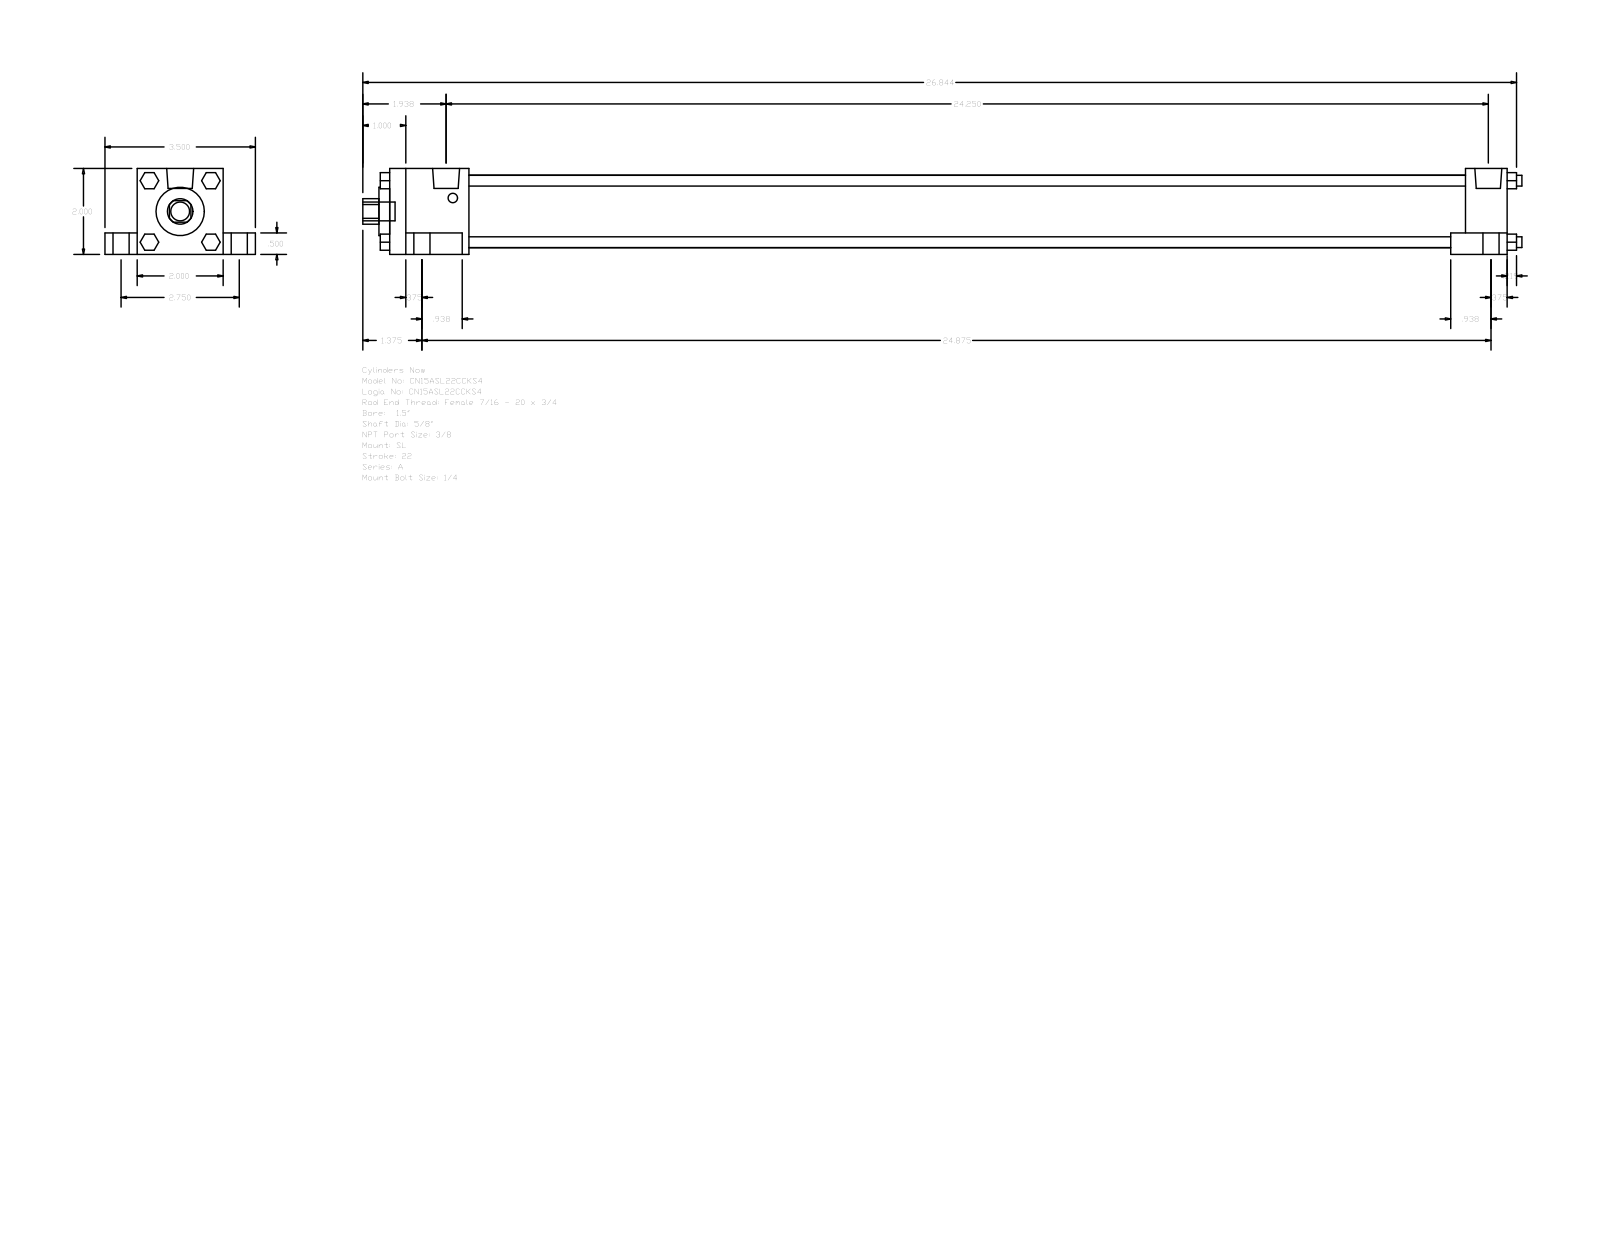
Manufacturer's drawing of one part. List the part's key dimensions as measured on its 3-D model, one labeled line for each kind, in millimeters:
Part name (STEP PRODUCT): A_SL__0150_0.625
STEP written by: GSSL Pune (CONFIG_CONTROL_DESIGN)
Units: millimetres
Bodies: 0 solids, 148 faces (112 planar, 36 cylindrical, 0 other)
Overall size (bounding box): 685.01 × 88.9 × 50.8
Round holes (diameter × count): ⌀15.88 ×1, ⌀28.57 ×1, ⌀42.93 ×1
Round bosses / shafts (diameter × count): ⌀15.88 ×4, ⌀9.53 ×4, ⌀6.35 ×4, ⌀5.56 ×4, ⌀15.93 ×2, ⌀11.11 ×1
Partial cylindrical surfaces — rounded edges, fillets, slot ends (radius × count): R7.54 ×1
Main face-to-face distances: 50.8, 19.05, 12.7, 38.1, 69.85, 660.39, 9.52, 635.79, 24.6, 46.83
